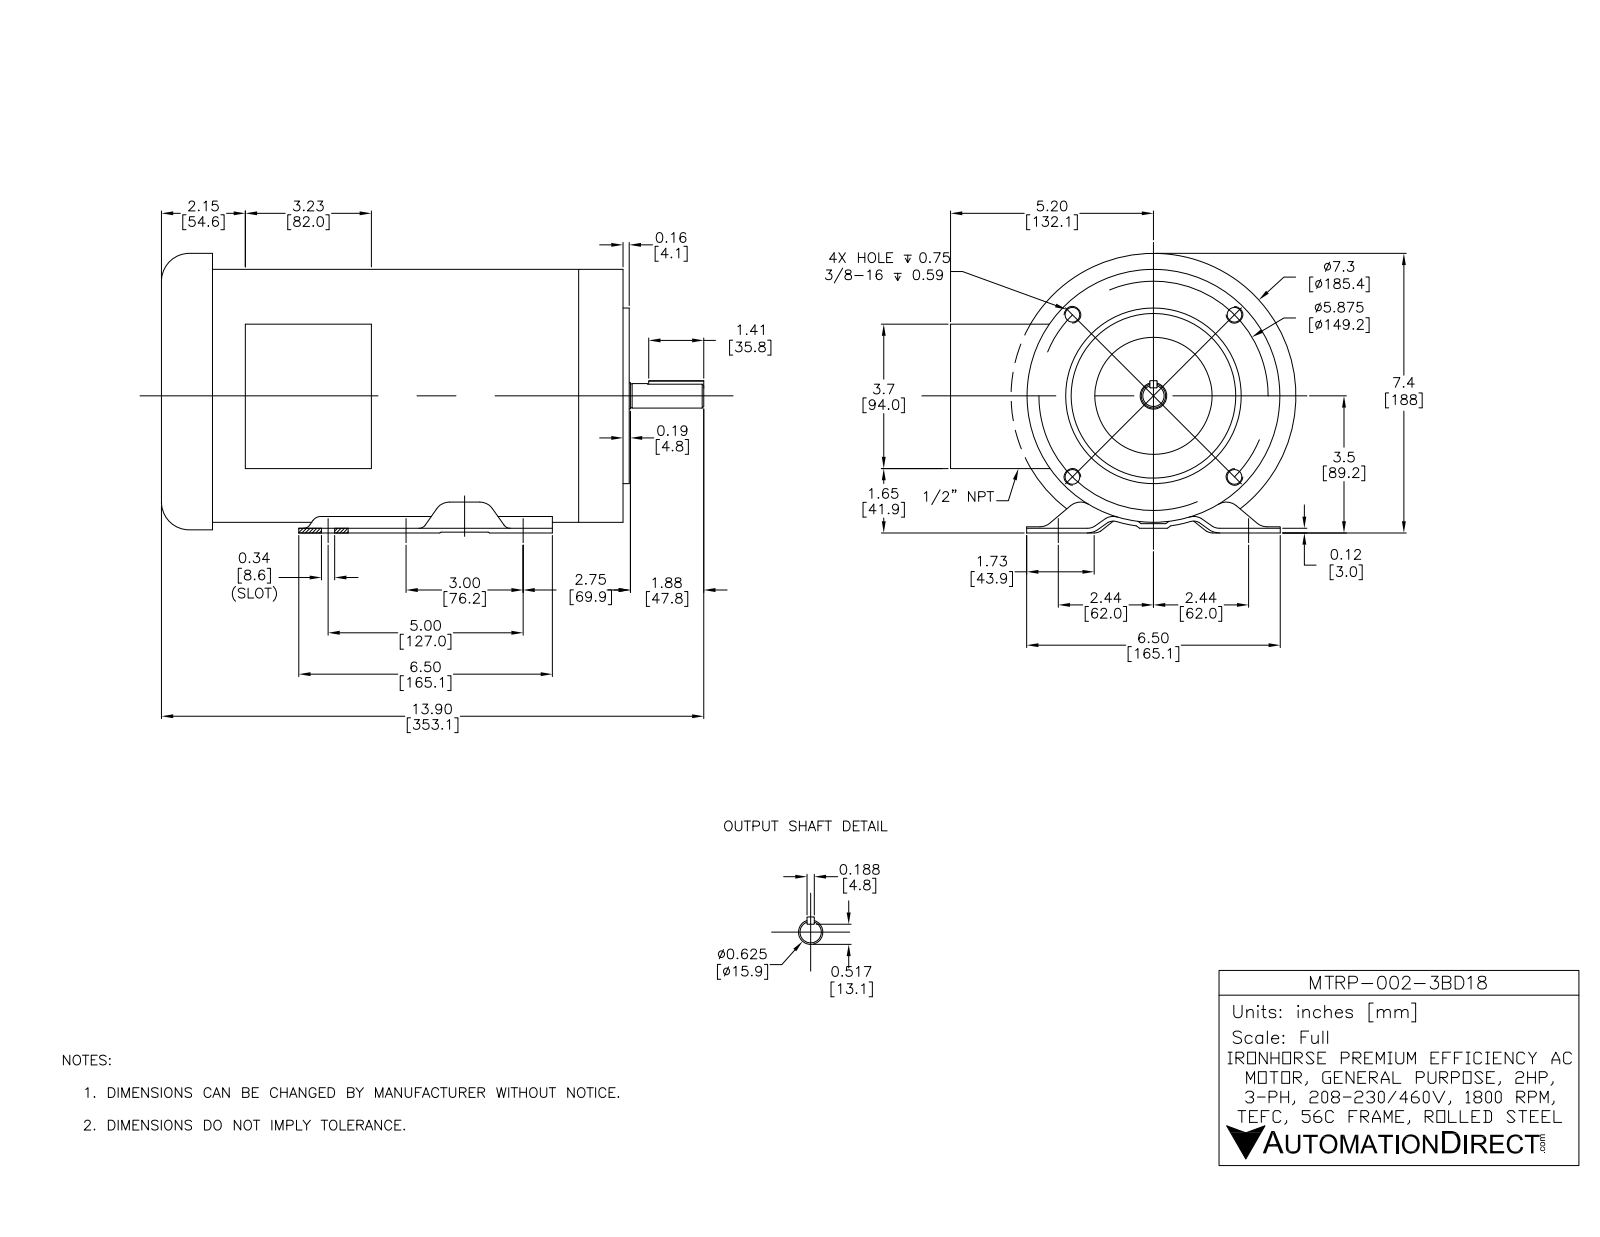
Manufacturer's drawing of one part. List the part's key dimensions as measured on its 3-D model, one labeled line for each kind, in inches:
Part name (STEP PRODUCT): MTRP-002-3BD18
STEP written by: SolidWorks 2021 (AUTOMOTIVE_DESIGN)
Units: inches
Bodies: 39 solids, 3603 faces (797 planar, 1141 cylindrical, 1665 other)
Overall size (bounding box): 13.72 × 8.938 × 7.234
Volume: 47.64 in³ · Surface area: 1 043 in²
Round holes (diameter × count): ⌀0.197 ×12, ⌀0.219 ×9, ⌀0.276 ×8, ⌀0.217 ×6, ⌀0.273 ×6, ⌀0.344 ×6, ⌀0.136 ×5, ⌀0.15 ×4, ⌀0.177 ×4, ⌀0.313 ×4, ⌀0.067 ×2, ⌀0.134 ×2
Round bosses / shafts (diameter × count): ⌀0.164 ×9, ⌀0.414 ×6, ⌀0.348 ×6, ⌀0.25 ×6, ⌀0.19 ×6, ⌀0.348 ×3, ⌀7.185 ×1, ⌀6.457 ×1
Partial cylindrical surfaces — rounded edges, fillets, slot ends (radius × count): R0.02 ×204, R0.118 ×123, R0.079 ×43, R0.039 ×38, R0.157 ×32, R0.138 ×26, R0.276 ×19, R0.172 ×12
Main face-to-face distances: 0.118, 0.039, 0.063, 11.654, 11.614, 3.559, 0.079, 3.087, 0.047, 0.098
Hole centre spacings: 4.221, 3.031, 0.094, 2.32, 2.409, 2.937, 2.979, 3.748
